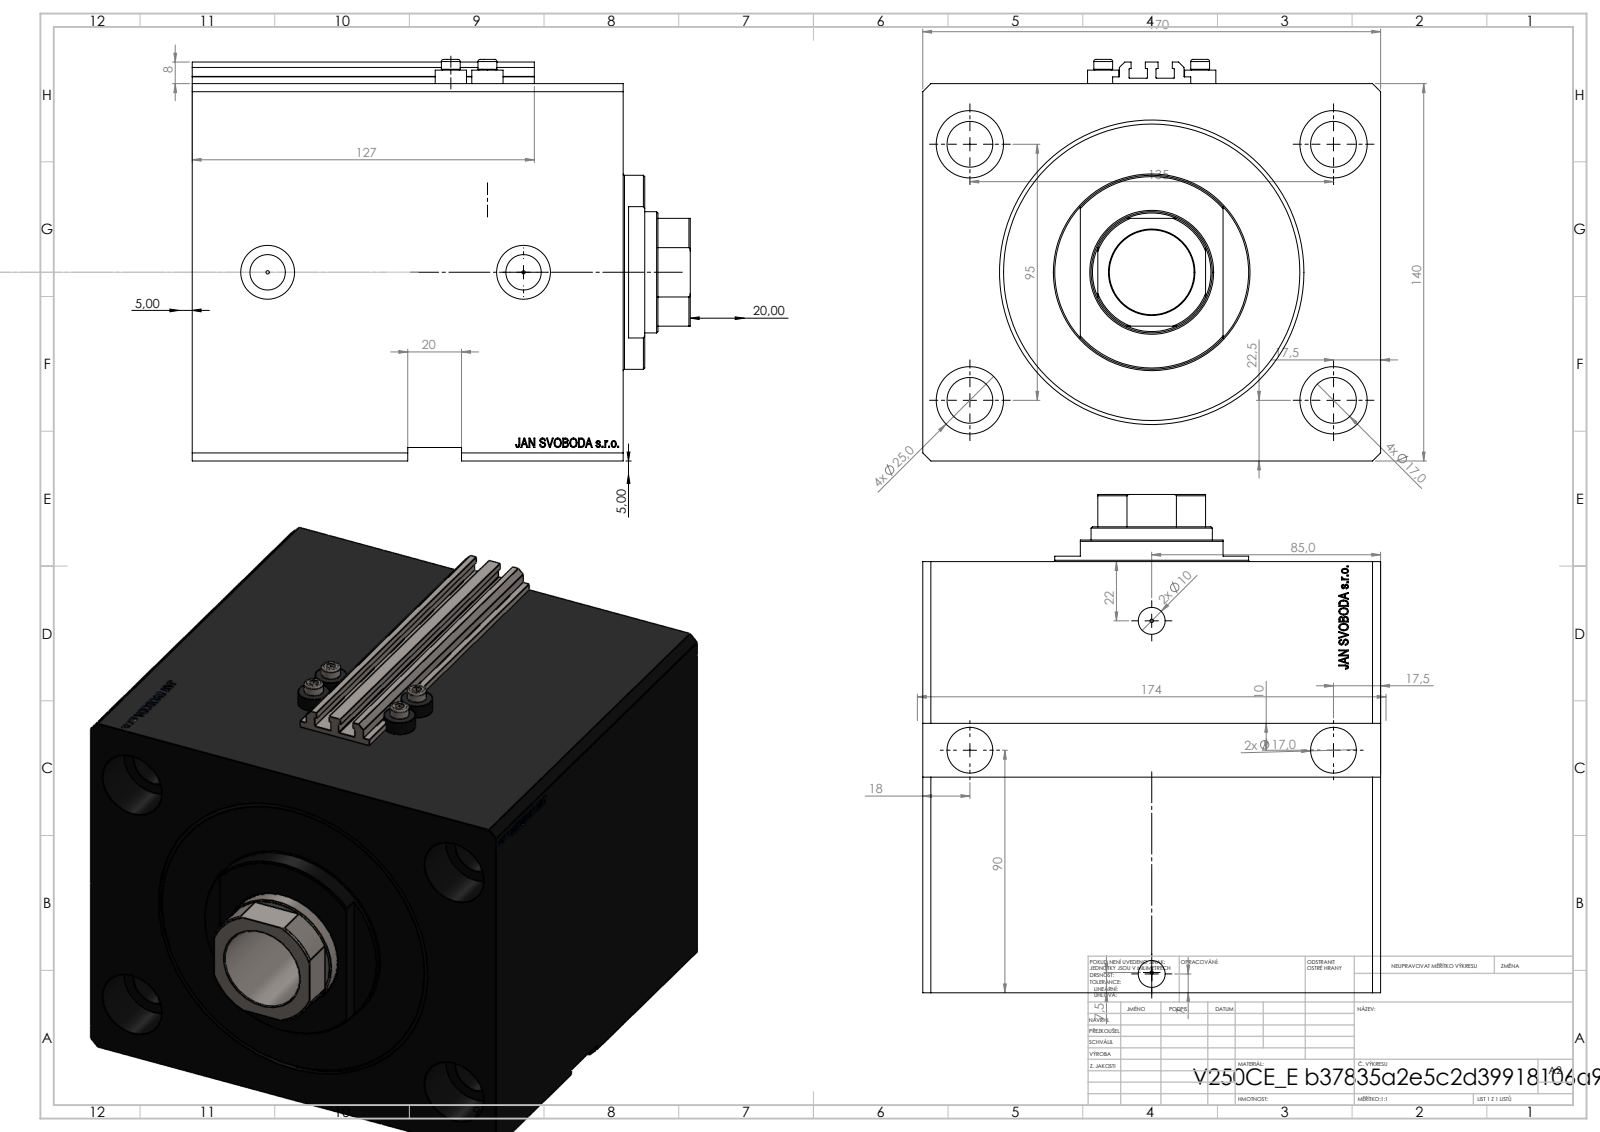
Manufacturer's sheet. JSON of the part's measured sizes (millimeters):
{"part_name": "V250CE_VC_E; V250CE_E_Body; V250CE_C_VCP; ALLEN BOLT V250CE", "step_written_by": "SolidWorks 2019 (CONFIG_CONTROL_DESIGN)", "units": "millimeters", "bodies": {"solids": 8, "faces": 1123, "planar": 547, "cylindrical": 138, "other": 438}, "overall_size": [185, 170, 149], "volume_mm3": 3230000, "surface_area_mm2": 344001, "round_holes": [[17, 8], [1.25, 4], [4, 4], [25, 4], [10, 2], [13.16, 2], [20, 2], [31.5, 1], [45, 1], [100, 1], [113, 1]], "round_bosses_or_shafts": [[11.6, 4], [7, 4], [72, 1]], "partial_cylinders_radius": [[0.2, 10], [22, 1]], "face_to_face_distances": [140, 170, 160, 28.9, 131.1, 135, 25, 106.1, 50, 85], "hole_center_spacings": [82.54, 135, 95, 13.6, 30, 33.62, 36, 38.48]}
